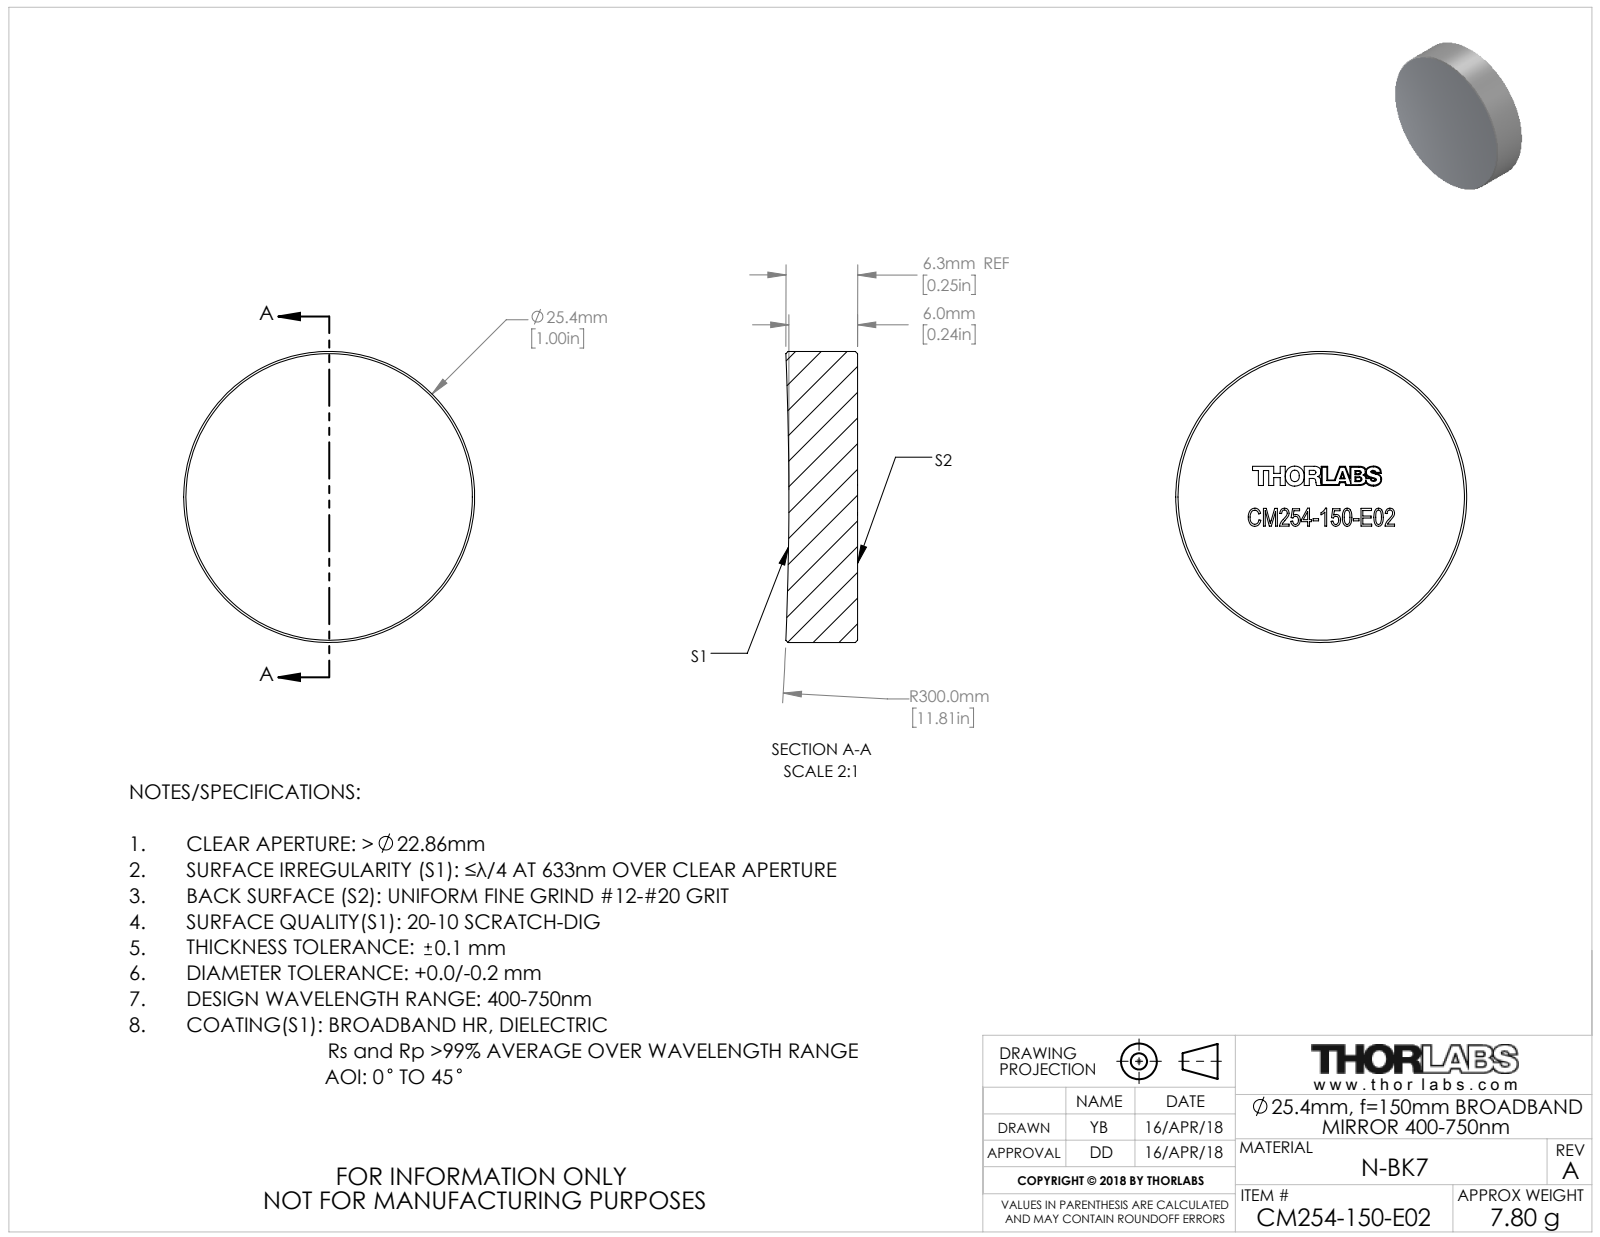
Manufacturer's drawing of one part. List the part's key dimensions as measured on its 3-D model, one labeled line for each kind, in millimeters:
Part name (STEP PRODUCT): TTN153277-E0W
STEP written by: SolidWorks 2018 (CONFIG_CONTROL_DESIGN)
Units: millimetres
Bodies: 1 solid, 40 faces (32 planar, 2 cylindrical, 6 other)
Overall size (bounding box): 25.4 × 25.4 × 6.26
Volume: 3 105 mm³ · Surface area: 1 495 mm²
Round bosses / shafts (diameter × count): ⌀25.4 ×1
